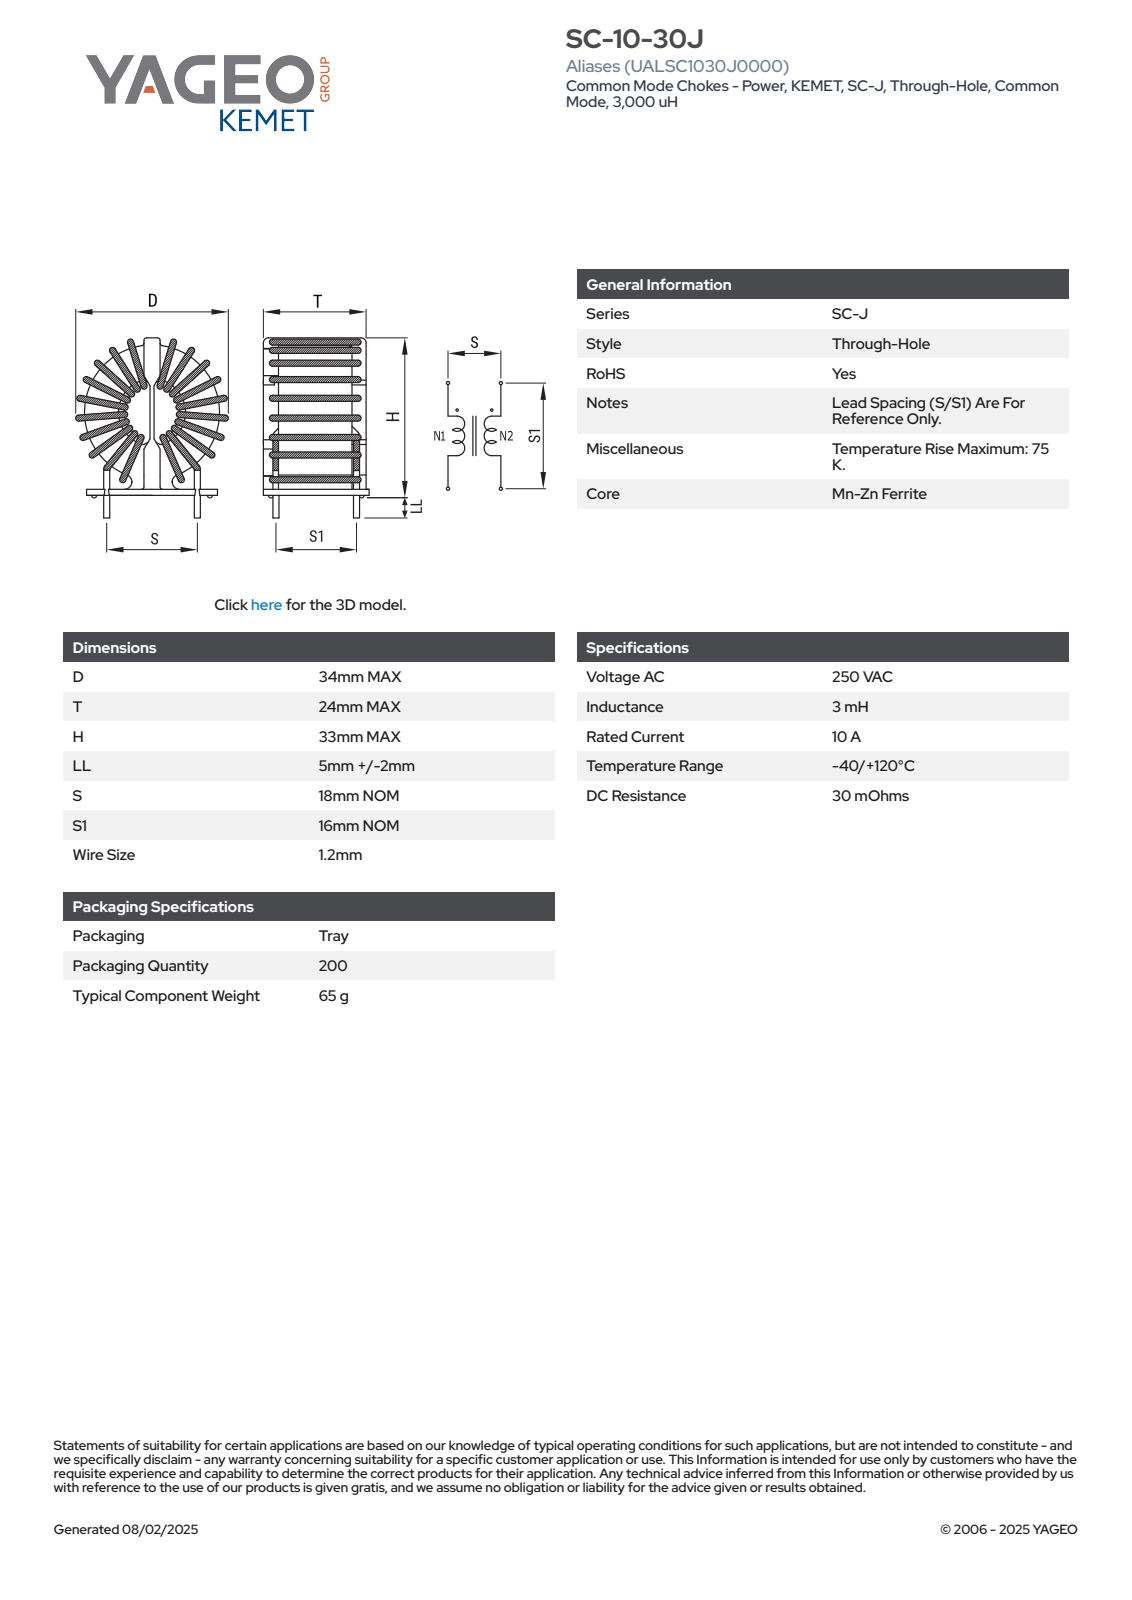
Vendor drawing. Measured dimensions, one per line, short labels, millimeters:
name: SC-10-30J
written by: SolidWorks 2018 (AUTOMOTIVE_DESIGN)
unit: mm
bodies: 1 solid, 377 faces (165 planar, 128 cylindrical, 84 other)
size: 40 × 34 × 24
volume: 14 614 mm³; area: 7 865 mm²
bosses: 8× ⌀1.2, 4× ⌀1
rounds: 22× R0.5, 16× R0.6, 6× R1, 4× R0.7, 4× R1.5, 1× R4.5, 1× R6.64, 1× R7.35
face distances: 1.2, 19, 0.8, 16.8, 2.2, 2, 12.1, 3, 14.6, 4.7
